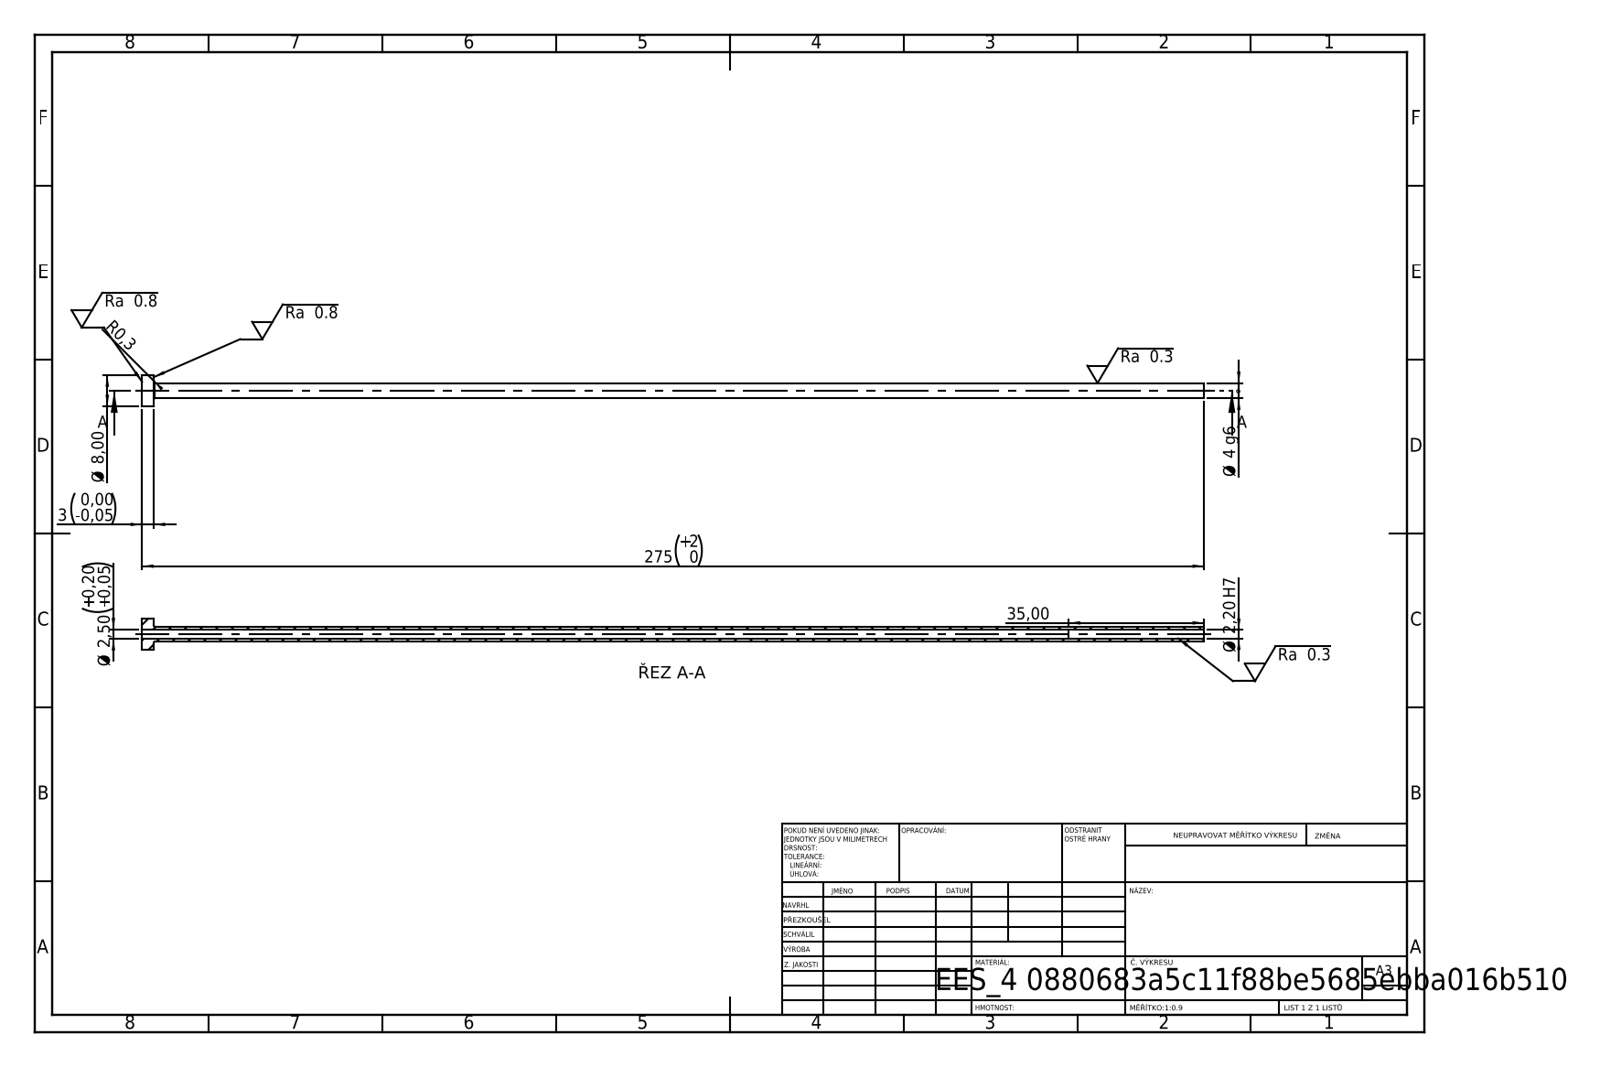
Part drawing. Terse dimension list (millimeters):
written by: SolidWorks 2019 (CONFIG_CONTROL_DESIGN)
unit: mm
bodies: 1 solid, 14 faces (4 planar, 8 cylindrical, 2 other)
size: 275 × 8 × 8
volume: 2 258 mm³; area: 5 712 mm²
holes: 1× ⌀2.2, 1× ⌀2.5
bosses: 1× ⌀8, 1× ⌀4
face distances: 3, 275, 272, 240, 237, 35
